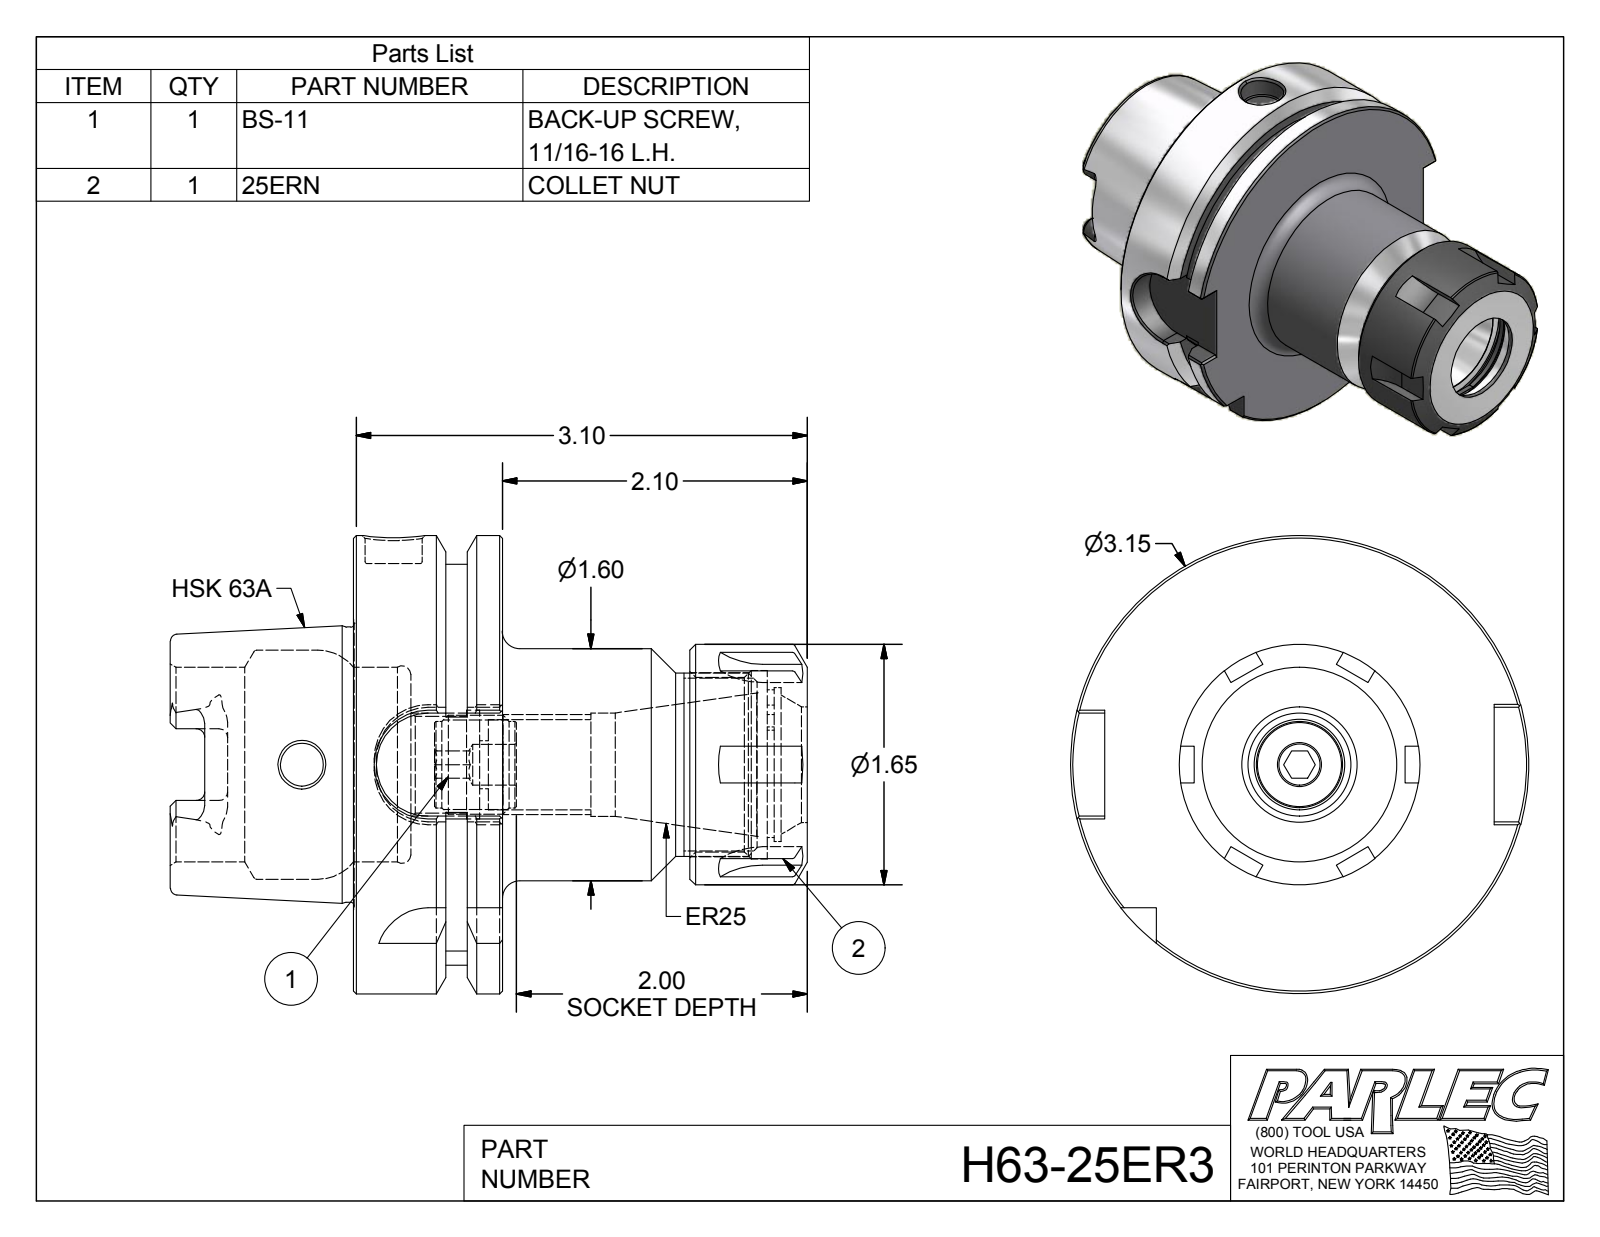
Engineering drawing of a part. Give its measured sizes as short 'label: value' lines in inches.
name: H63-25ER3; H63-25ER3-1; BS-11; 25ERN
written by: Autodesk Inventor 2012 (AUTOMOTIVE_DESIGN)
unit: in
bodies: 3 solids, 213 faces (91 planar, 55 cylindrical, 67 other)
size: 4.38 × 3.15 × 3.15
volume: 10.96 in³; area: 67.45 in²
holes: 1× ⌀0.28, 1× ⌀0.295, 1× ⌀0.331, 1× ⌀0.394, 1× ⌀0.62, 1× ⌀0.666, 1× ⌀0.71, 1× ⌀0.749, 1× ⌀0.794, 1× ⌀1.057, 1× ⌀1.201, 1× ⌀1.294
bosses: 1× ⌀3.15, 1× ⌀1.891, 1× ⌀1.654, 1× ⌀1.595, 1× ⌀1.26, 1× ⌀0.681, 1× ⌀0.595
rounds: 6× R0.059, 6× R0.5, 4× R0.113, 4× R0.354, 1× R0.472, 1× R0.515, 1× R1.378
face distances: 1.024, 0.241, 0.389, 3.12, 2.096, 0.394, 0.63, 2.726, 0.783, 2.337
